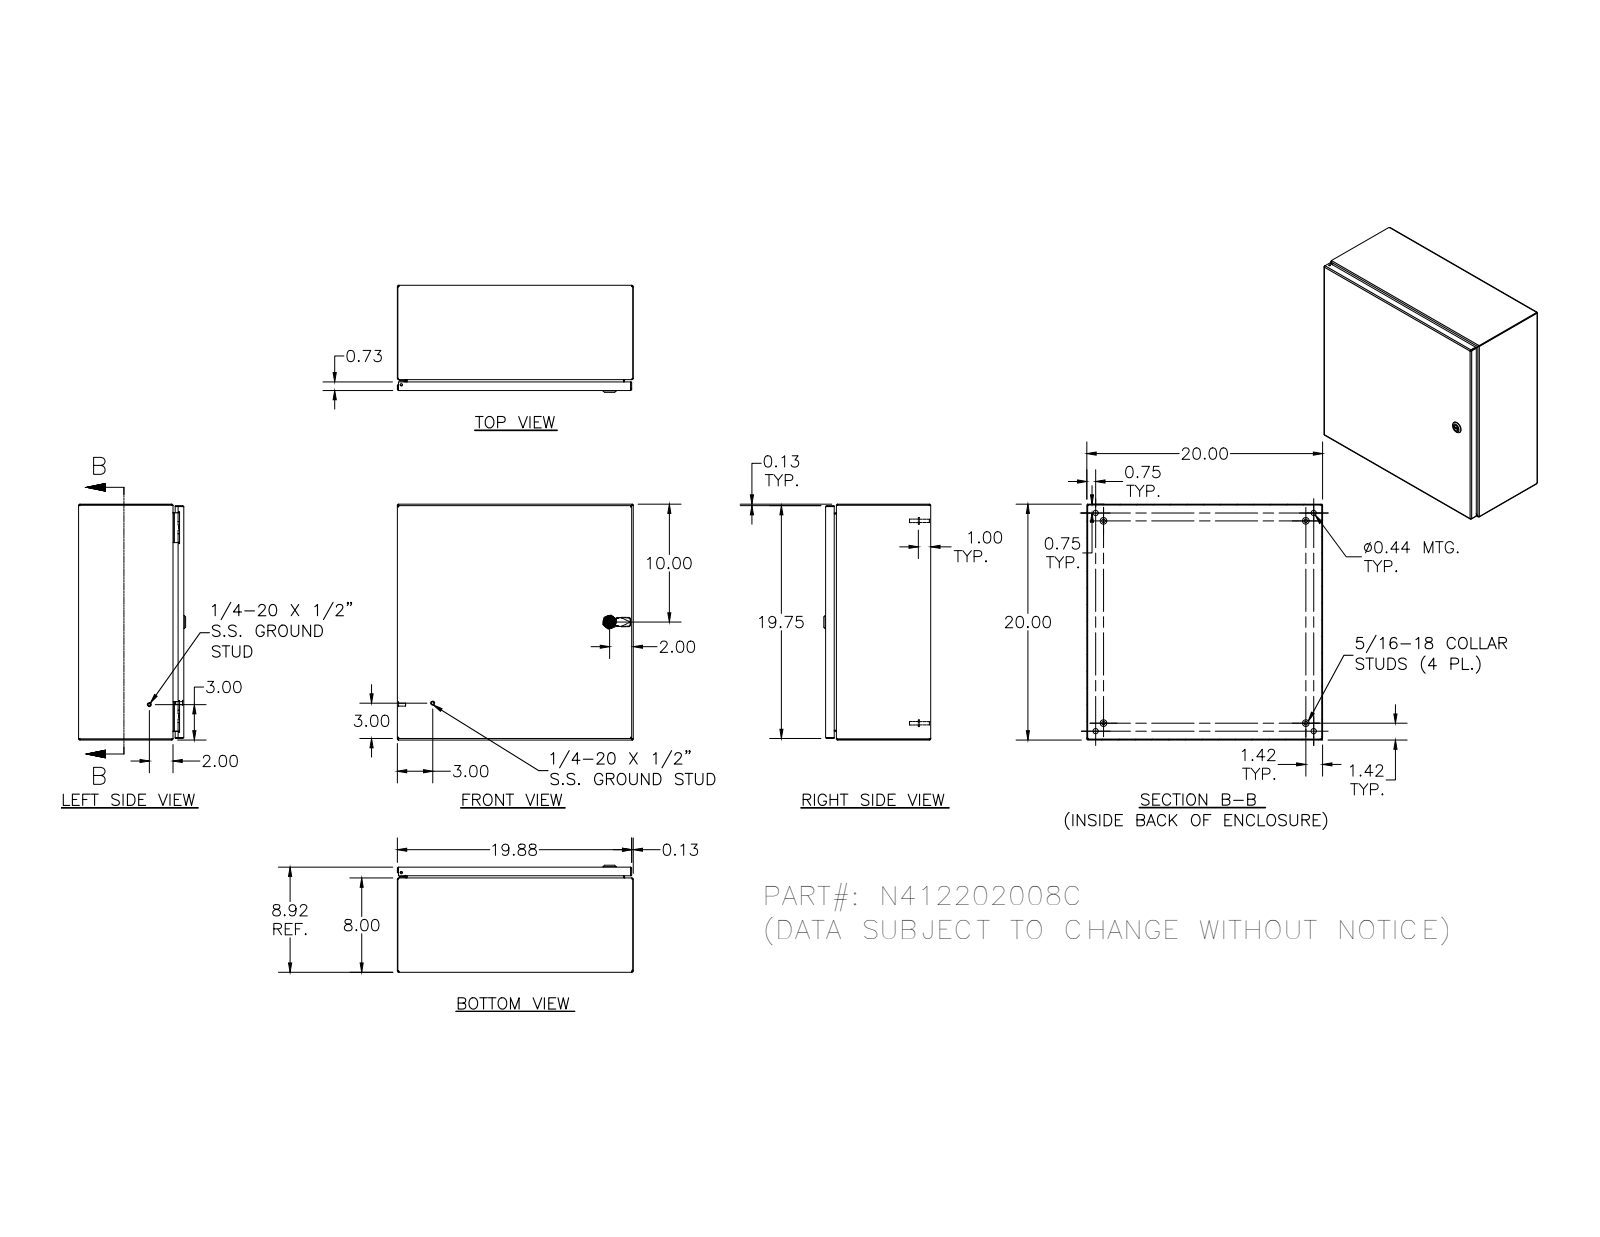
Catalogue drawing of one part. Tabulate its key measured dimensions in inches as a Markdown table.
| quantity | value |
| --- | --- |
| part name | N412202008C |
| STEP written by | SolidWorks 2018 (AUTOMOTIVE_DESIGN) |
| units | inches |
| bodies | 33 solids, 1449 faces (530 planar, 547 cylindrical, 372 other) |
| overall size | 20 × 20 × 9.075 |
| volume | 118.6 in³ |
| surface area | 3 225 in² |
| round holes (diameter × count) | 0.188 × 5, 0.093 × 4, 0.152 × 4, 0.167 × 4, 0.172 × 4, 0.437 × 4, 0.156 × 2, 0.187 × 1, 0.197 × 1, 0.315 × 1, 0.394 × 1, 0.402 × 1 |
| round bosses / shafts (diameter × count) | 0.25 × 10, 0.131 × 5, 0.563 × 4, 0.36 × 4, 0.32 × 4, 0.3 × 4, 0.275 × 4, 0.256 × 4 |
| partial cylindrical surfaces (radius × count) | 0.012 × 30, 0.031 × 30, 0.05 × 26, 0.105 × 20, 0.016 × 18, 0.125 × 16, 0.02 × 13, 0.032 × 8 |
| main face-to-face distances | 0.074, 8.843, 8.769, 8.917, 19.926, 19.852, 0.074, 19.926, 20, 0.917 |
| hole center spacings | 16, 0.66, 0.656, 1.307, 1.965, 15.34, 15.996, 16.656 |
